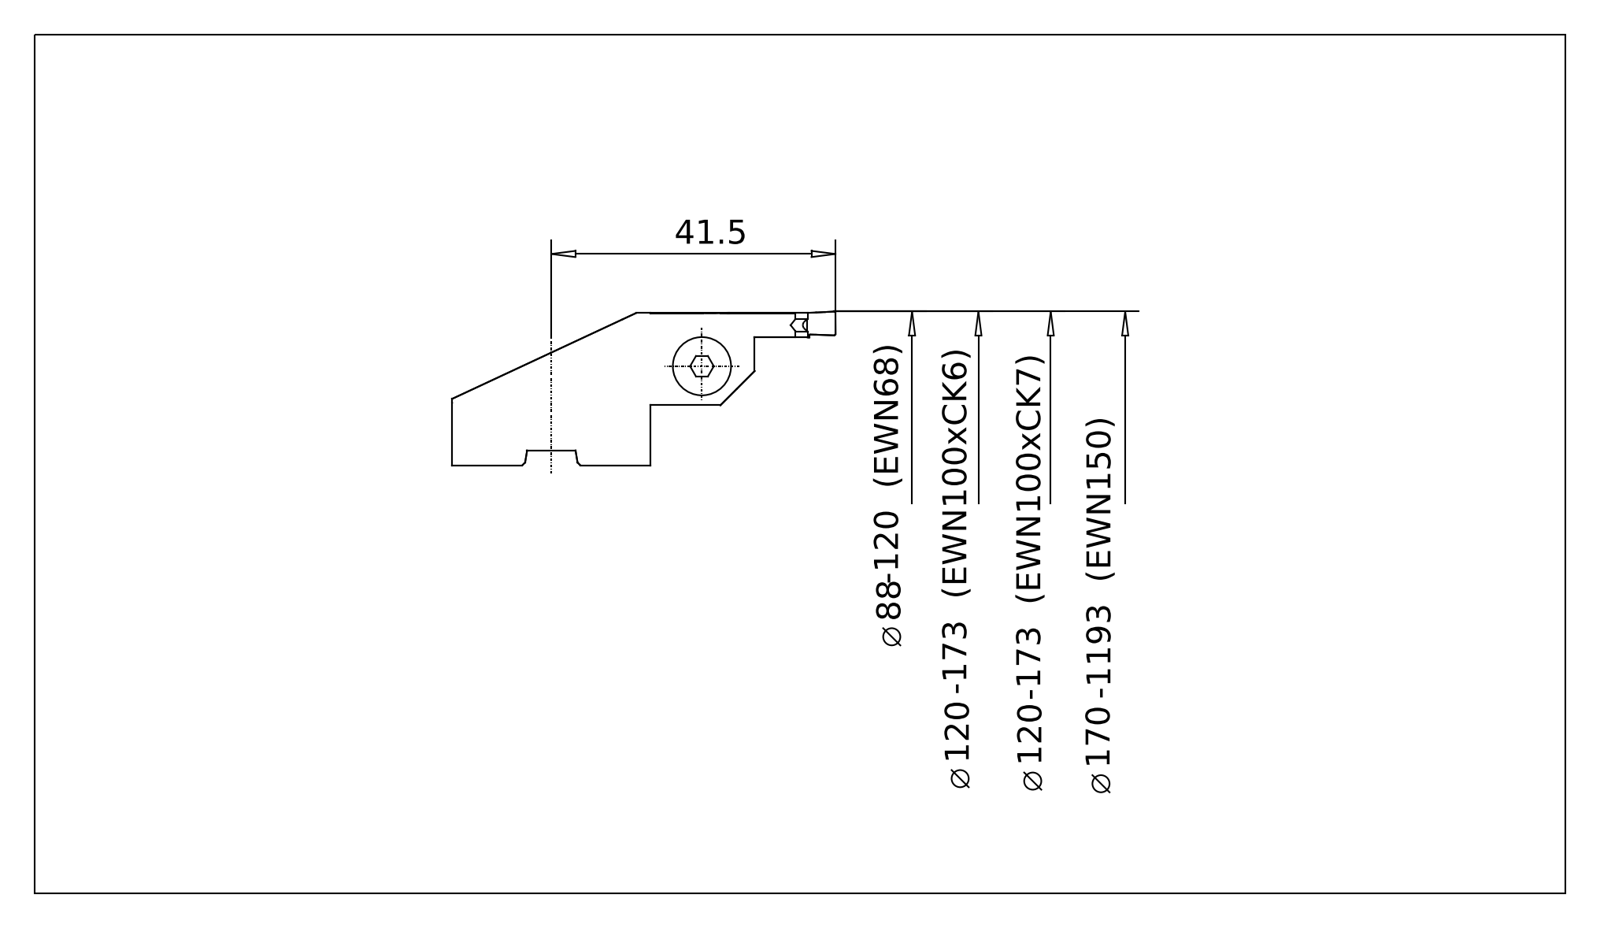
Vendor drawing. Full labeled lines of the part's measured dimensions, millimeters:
Part name (STEP PRODUCT): 626.946 Kaiser ENH 62 S4 88-120 R|958.425 Kaiser NP 4250 P20C_Einstechplatte 4mm;NONE; 626.946 Kaiser ENH 62 S4 88-120 R|626.946 Kaiser ENH 62 S4 88-120 R;Fase21; 626.946 Kaiser ENH 62 S4 88-120 R|690.183 Kaiser ETL M5x12A;Verrundung1
STEP written by: ACIS (automotive_design)
Units: millimetres
Bodies: 3 solids, 136 faces (79 planar, 39 cylindrical, 18 other)
Overall size (bounding box): 56 × 29 × 22.43
Volume: 12 967 mm³ · Surface area: 6 006 mm²
Round holes (diameter × count): ⌀4.2 ×1, ⌀5.3 ×1, ⌀8.05 ×1, ⌀9 ×1, ⌀14 ×1
Round bosses / shafts (diameter × count): ⌀29 ×1, ⌀8.5 ×1, ⌀5 ×1
Partial cylindrical surfaces — rounded edges, fillets, slot ends (radius × count): R0.2 ×4, R0.1 ×2, R1.4 ×2, R1.63 ×2, R1.26 ×1, R5 ×1, R43.5 ×1
Main face-to-face distances: 8.75, 6.6, 2.15, 15, 1.6, 13.4, 7.8, 2.65, 3.95, 6.1
Hole centre spacings: 11.41
